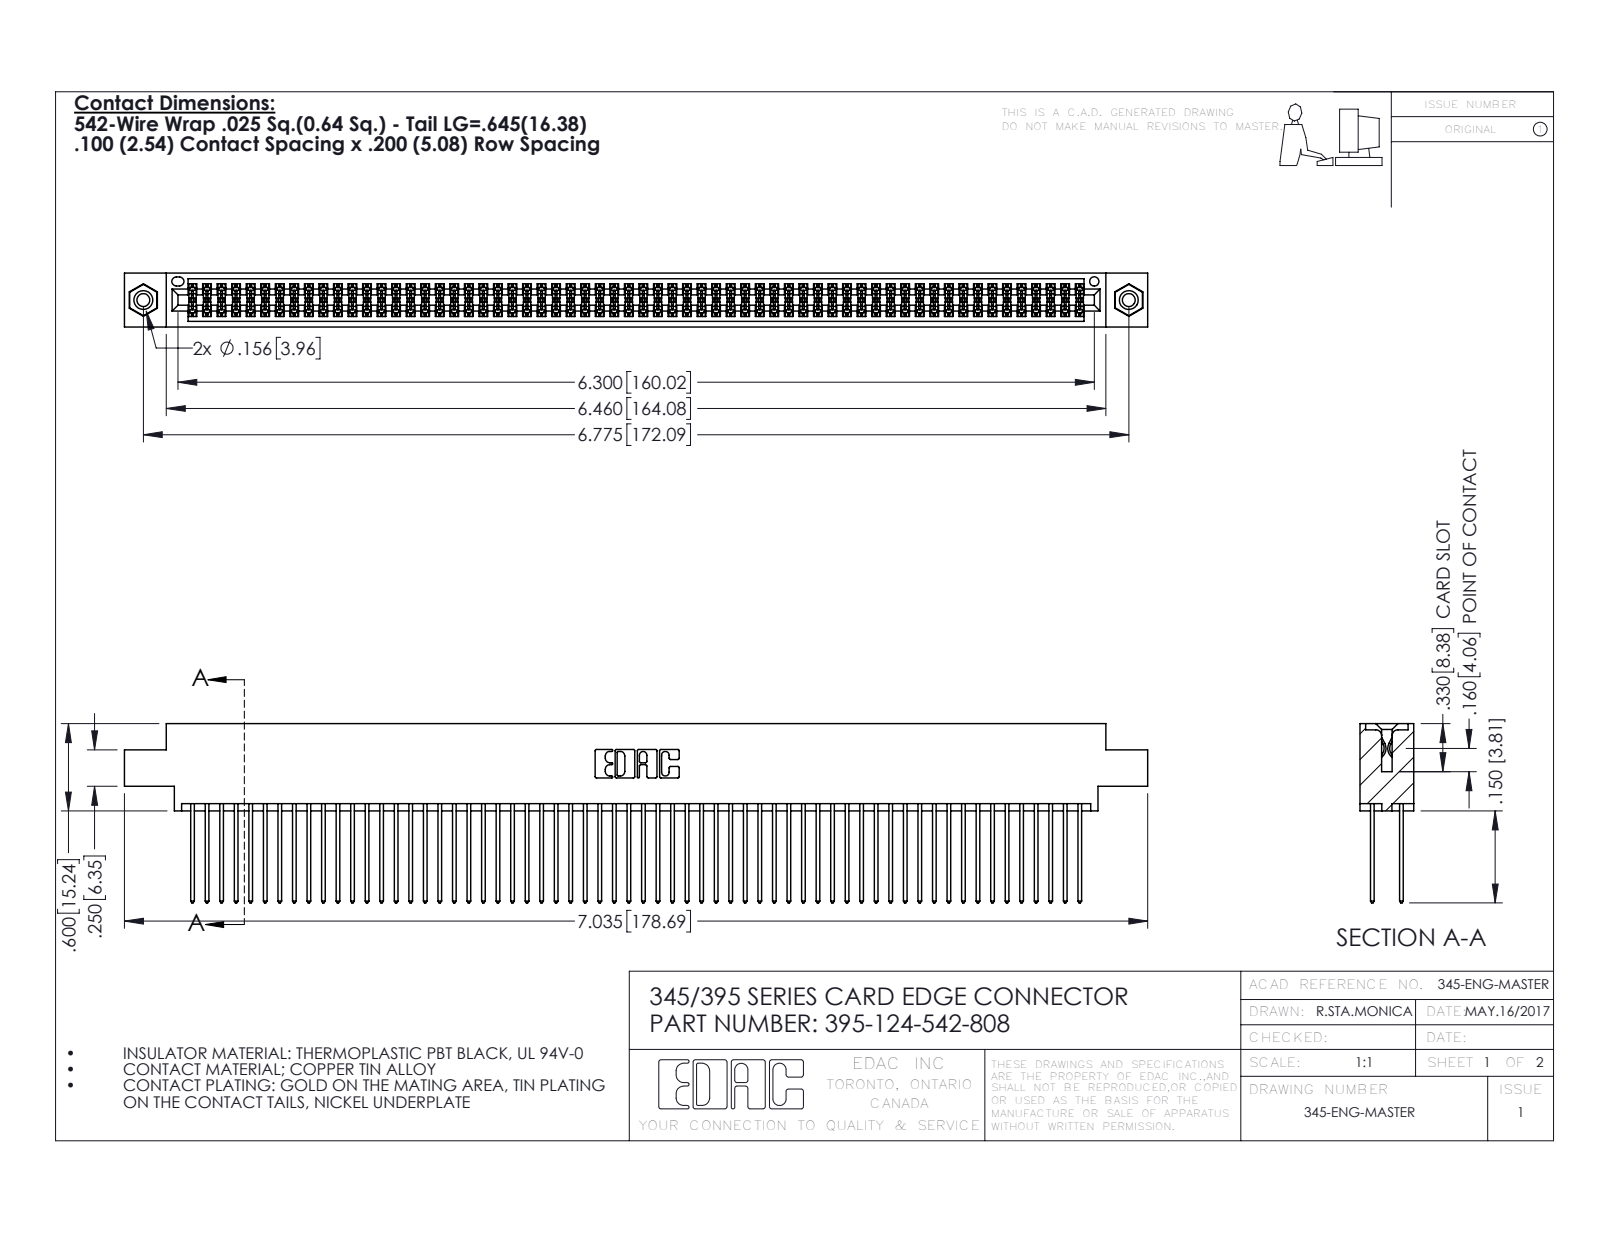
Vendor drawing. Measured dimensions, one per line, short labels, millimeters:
name: 395-124-542-808; 345 Part_0.170 Offset - 0.156 Dia-TI; 345-250-001_345-250-003-102; 345-292-001_345-293-142
written by: SolidWorks 2016 (CONFIG_CONTROL_DESIGN)
unit: mm
bodies: 127 solids, 6390 faces (4208 planar, 2166 cylindrical, 16 other)
size: 178.7 × 31.3 × 9.4
volume: 18 010 mm³; area: 29 860 mm²
holes: 2× ⌀2.3, 2× ⌀3.2, 2× ⌀4, 1× ⌀1.6
bosses: 2× ⌀3.9
rounds: 186× R0.2, 124× R0.3, 22× R0.3, 6× R0.2, 6× R0.8, 3× R0.7, 2× R0.4, 2× R0.5
face distances: 1.8, 7.6, 5.1, 2.5, 6.9, 0.6, 9.4, 5.7, 4.4, 3.8
hole spacings: 6.9, 166.1, 172.1
